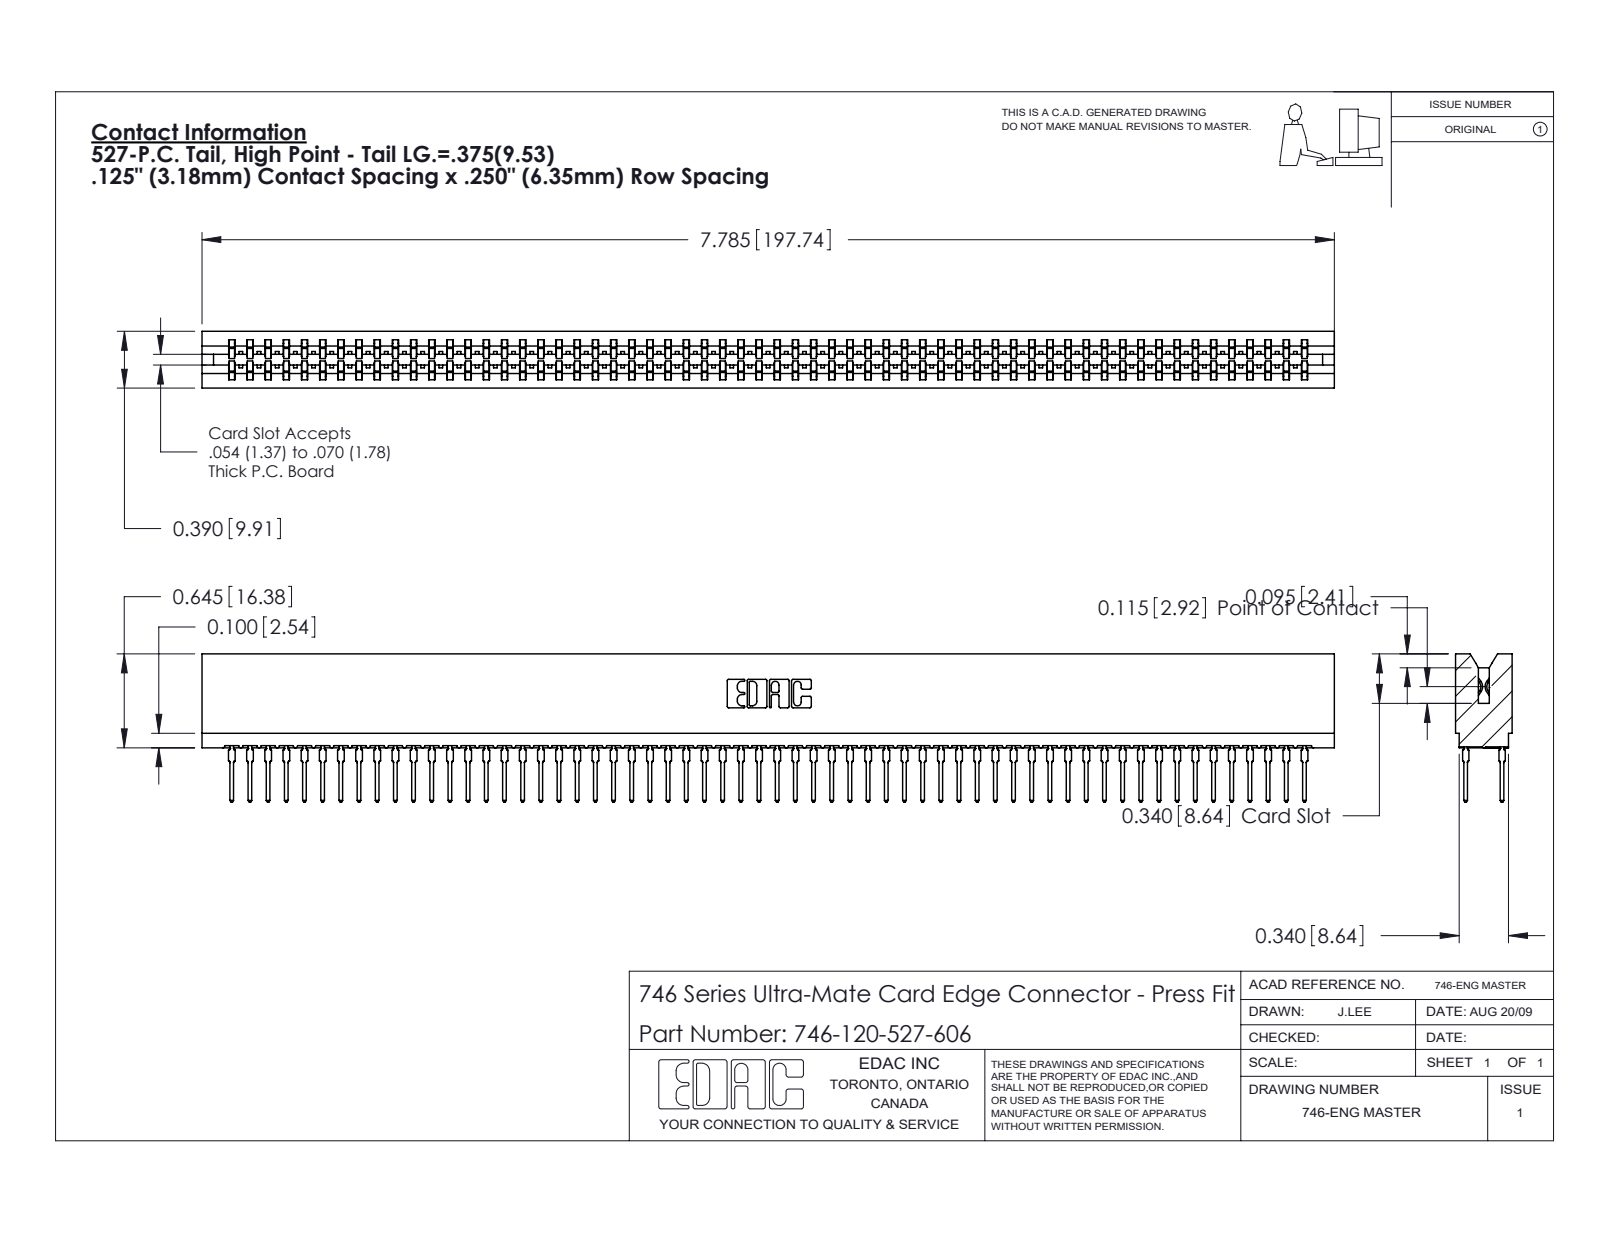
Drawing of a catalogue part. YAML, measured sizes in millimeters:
part_name: "746-120-527-606; 746-292-001_527; 746 Part_.340 Slot Depth - 06"
step_written_by: "SolidWorks 2020 (CONFIG_CONTROL_DESIGN)"
units: millimeters
bodies: {solids: 121, faces: 10838, planar: 5576, cylindrical: 2142, other: 3120}
overall_size: [197.7, 25.9, 9.9]
volume: 22810
surface_area: 34740
partial_cylinders:
  - {radius: 0.5, count: 240}
  - {radius: 0.4, count: 61}
  - {radius: 0.3, count: 22}
  - {radius: 0.1, count: 8}
  - {radius: 0.3, count: 8}
  - {radius: 0.2, count: 6}
  - {radius: 0.8, count: 6}
  - {radius: 0.7, count: 3}
face_to_face_distances: [1.4, 8.5, 9.9, 0.6, 6.4, 7.8, 7, 2.1, 0.4, 1.5]
